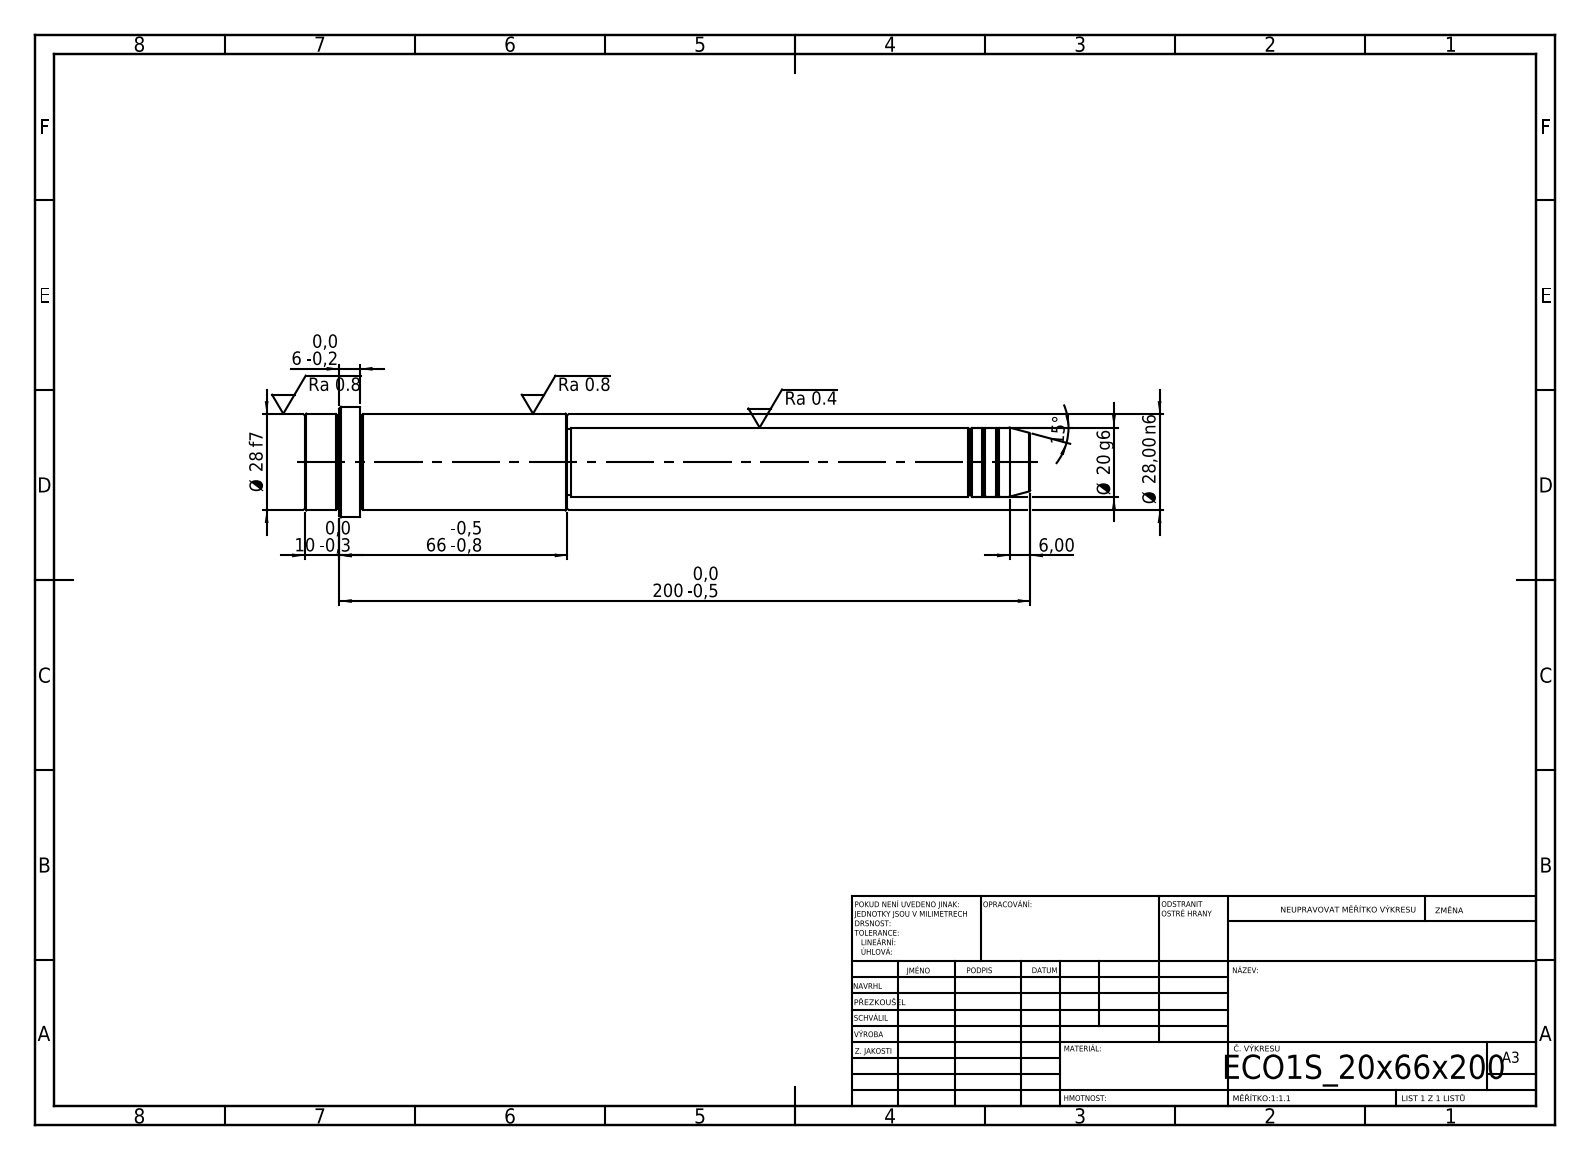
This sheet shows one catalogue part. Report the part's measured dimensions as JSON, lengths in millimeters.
{"step_written_by": "SolidWorks 2019 (CONFIG_CONTROL_DESIGN)", "units": "millimeters", "bodies": {"solids": 1, "faces": 52, "planar": 6, "cylindrical": 16, "other": 30}, "overall_size": [210, 32, 32], "volume_mm3": 89532, "surface_area_mm2": 16840, "round_bosses_or_shafts": [[32, 1], [28, 1], [20, 1], [19, 1]], "face_to_face_distances": [76, 134, 210, 194, 60, 16, 200, 66, 6, 10]}
